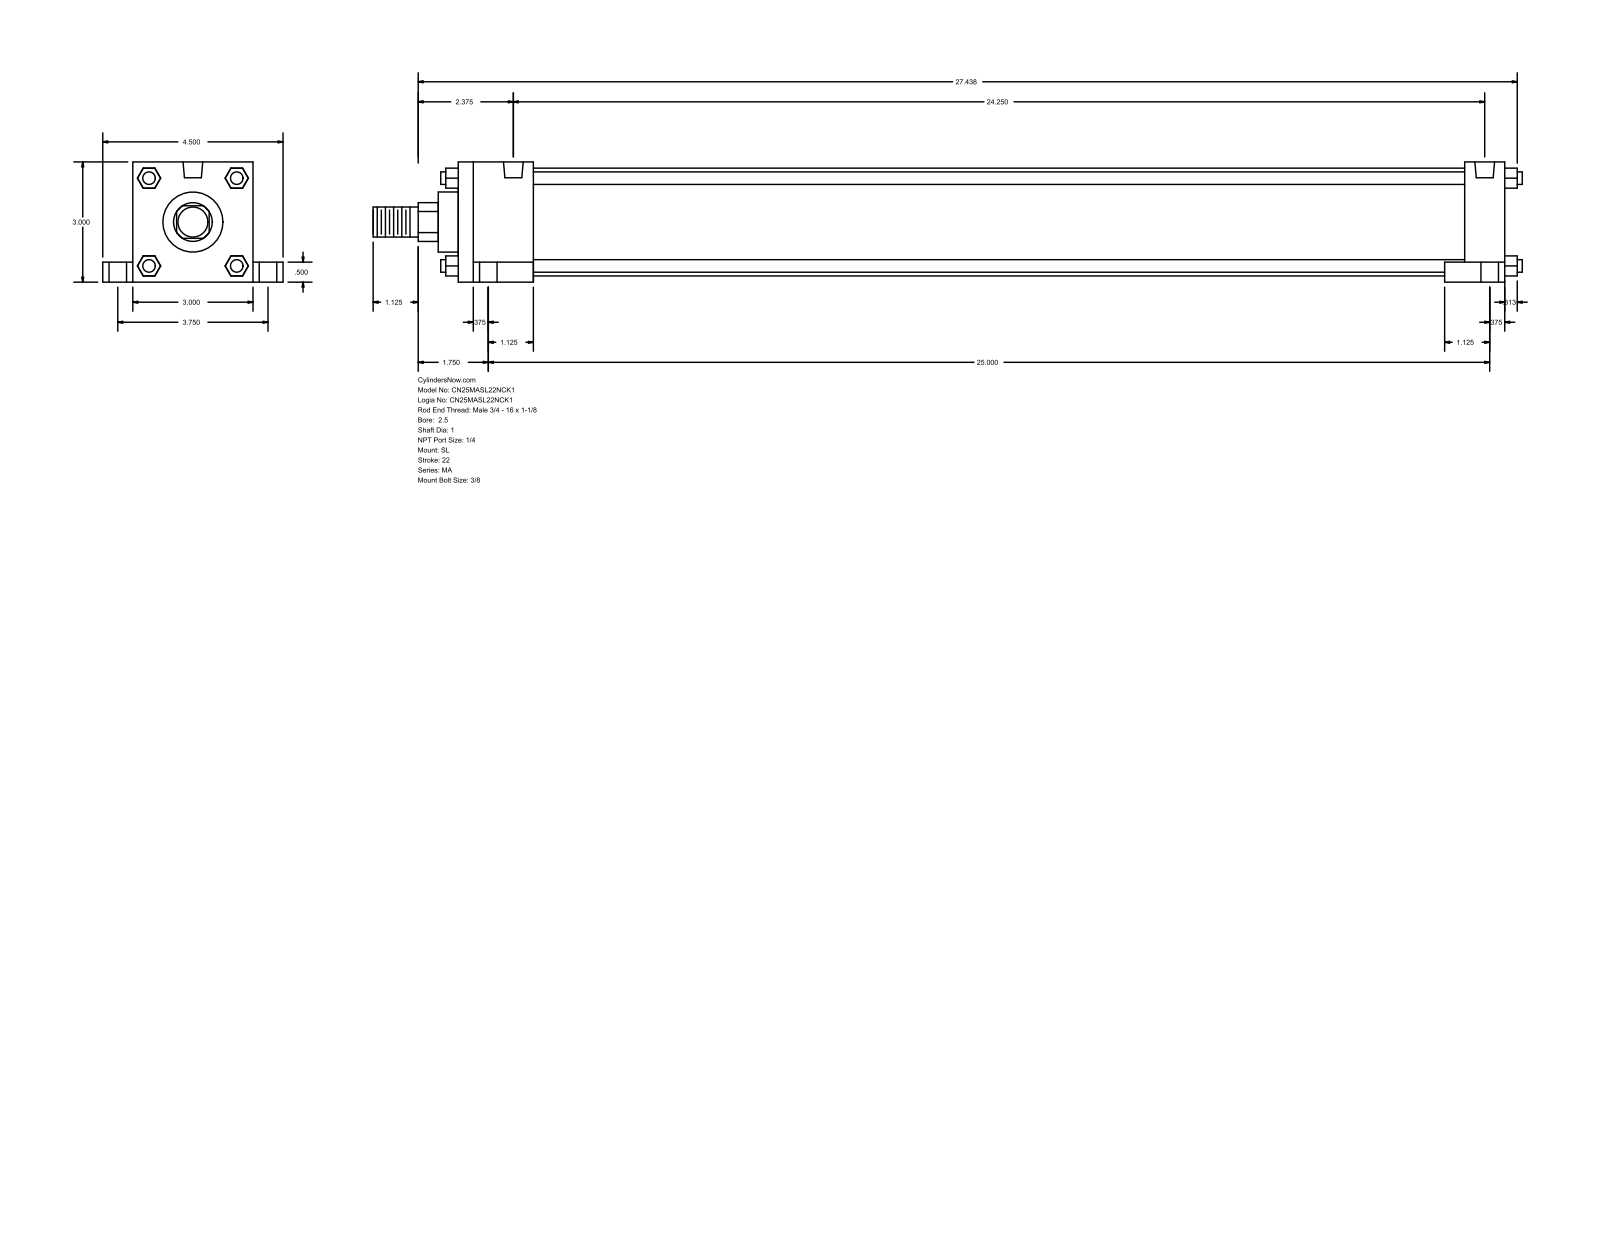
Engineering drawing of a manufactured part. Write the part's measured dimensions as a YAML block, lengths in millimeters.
part_name: "MA_SL__0250_1"
step_written_by: "GSSL Pune (CONFIG_CONTROL_DESIGN)"
units: millimeters
bodies: {solids: 0, faces: 148, planar: 112, cylindrical: 36, other: 0}
overall_size: [728.66, 114.3, 76.2]
round_holes:
  - {diameter: 7.94, count: 4}
  - {diameter: 11.11, count: 4}
  - {diameter: 17.46, count: 4}
  - {diameter: 12.49, count: 2}
round_bosses_or_shafts:
  - {diameter: 7.94, count: 4}
  - {diameter: 68.33, count: 1}
  - {diameter: 38.1, count: 1}
  - {diameter: 25.4, count: 1}
  - {diameter: 19.05, count: 1}
partial_cylinders:
  - {radius: 12.29, count: 1}
face_to_face_distances: [76.2, 663.58, 12.7, 590.55, 25.4, 47.63, 615.95, 638.18, 19.05, 95.25]
hole_center_spacings: [47.73, 50.2, 95.24, 615.94, 620.95, 633.61, 635, 642.1]
